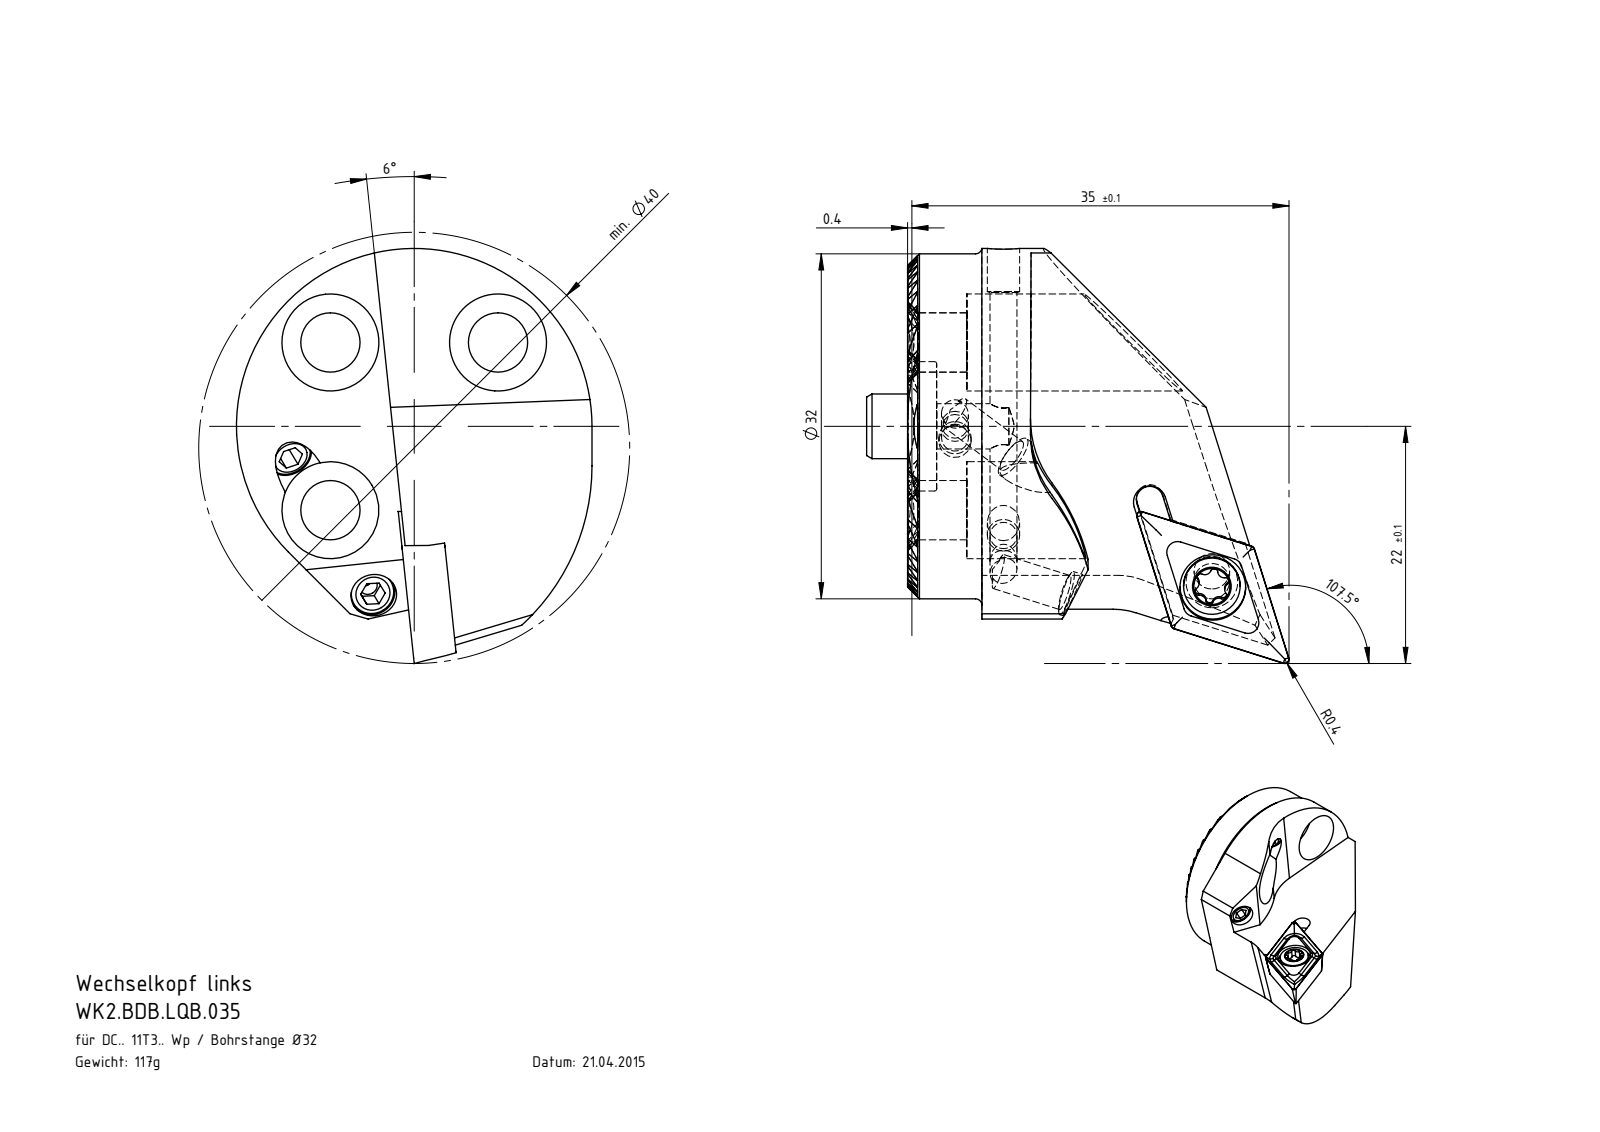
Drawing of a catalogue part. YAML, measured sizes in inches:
part_name: "WCB-ER2.001.009_A; WK2-BDB.LQB.035_A; WK2-ER1.001.012_A_Fertigbearbeitung; WK2.BDB.LQB.035 (+3 more)"
step_written_by: "SolidWorks 2017 (AUTOMOTIVE_DESIGN)"
units: inches
bodies: {solids: 12, faces: 564, planar: 196, cylindrical: 190, other: 178}
overall_size: [1.543, 1.516, 1.299]
volume: 0.89
surface_area: 12.38
round_holes:
  - {diameter: 0.094, count: 3}
  - {diameter: 0.098, count: 3}
  - {diameter: 0.13, count: 3}
  - {diameter: 0.165, count: 3}
  - {diameter: 0.217, count: 3}
  - {diameter: 0.354, count: 3}
  - {diameter: 0.067, count: 2}
  - {diameter: 0.118, count: 1}
  - {diameter: 0.173, count: 1}
  - {diameter: 0.24, count: 1}
  - {diameter: 0.472, count: 1}
round_bosses_or_shafts:
  - {diameter: 0.157, count: 3}
  - {diameter: 0.118, count: 3}
  - {diameter: 1.26, count: 1}
  - {diameter: 0.236, count: 1}
  - {diameter: 0.207, count: 1}
partial_cylinders:
  - {radius: 0.005, count: 22}
  - {radius: 0.013, count: 6}
  - {radius: 0.023, count: 6}
  - {radius: 0.787, count: 2}
  - {radius: 0.049, count: 1}
  - {radius: 0.276, count: 1}
  - {radius: 0.394, count: 1}
  - {radius: 0.65, count: 1}
face_to_face_distances: [0.051, 0.102, 0.154, 0.205, 0.256, 0.511, 0.46, 0.563, 0.307, 0.409]
hole_center_spacings: [0.433, 0.613, 0.867]
